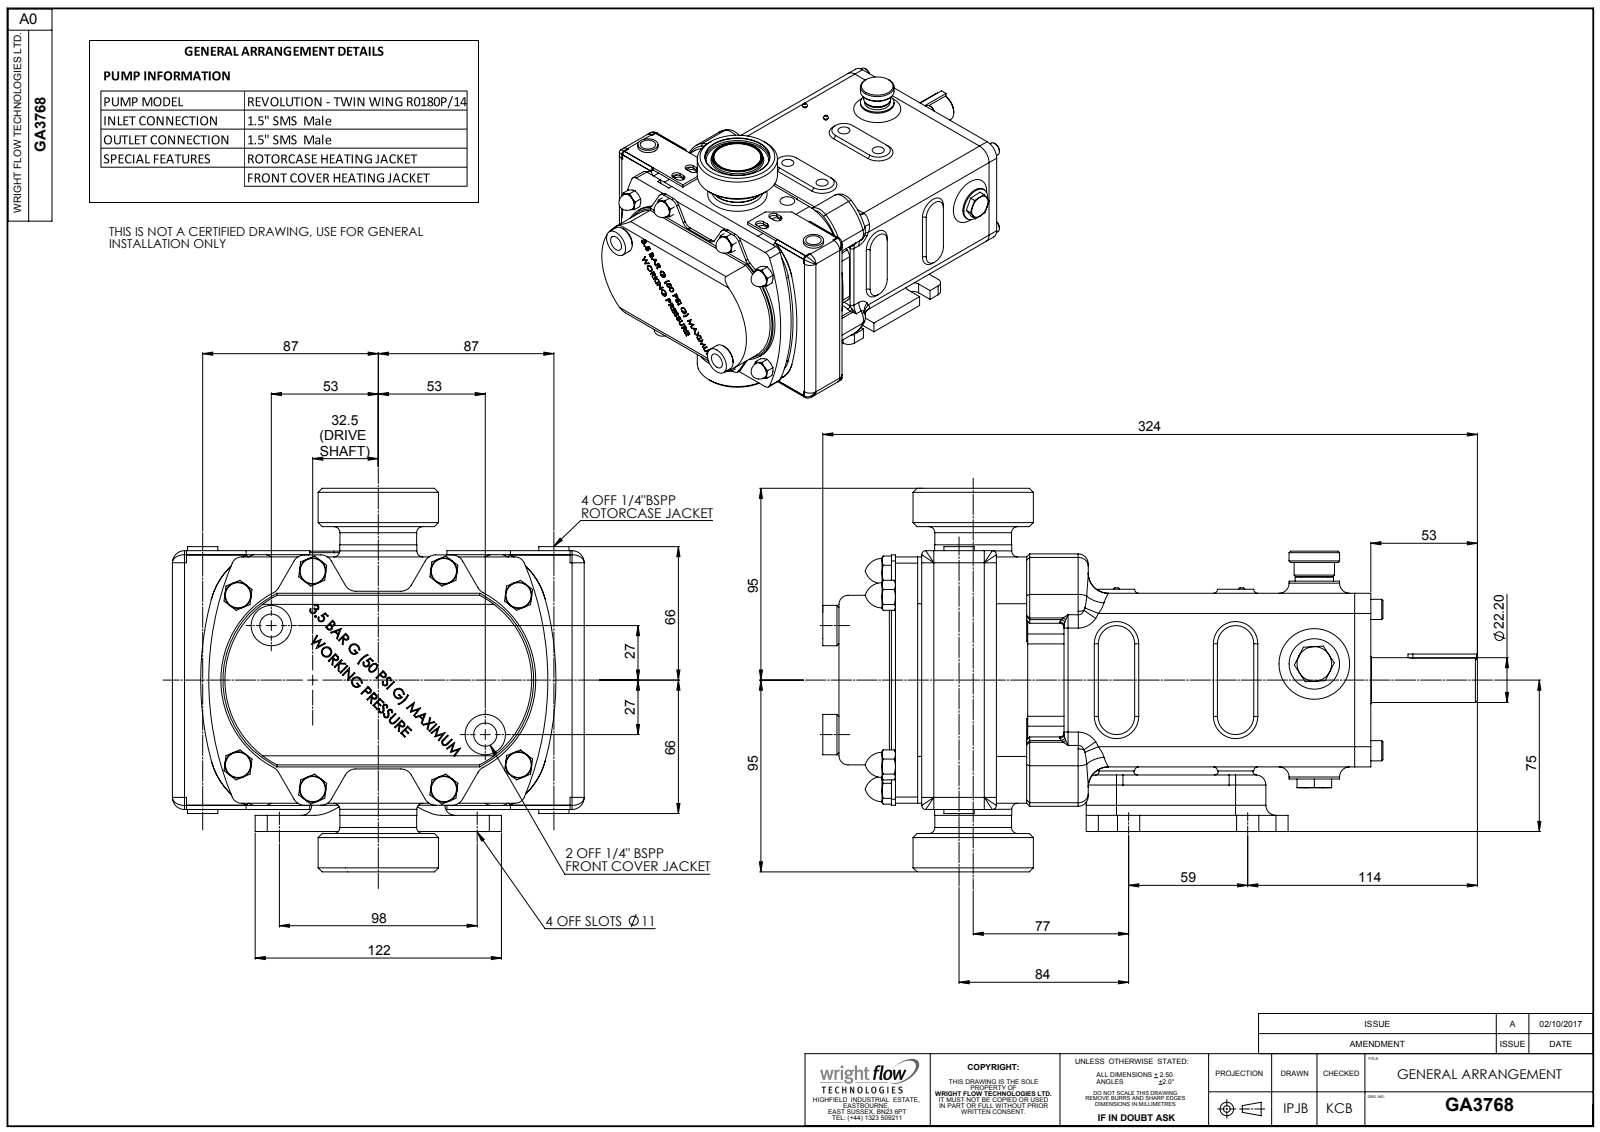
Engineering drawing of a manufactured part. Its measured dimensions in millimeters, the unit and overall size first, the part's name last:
Units: millimetres
Overall size (bounding box): 324.3 × 204 × 190
Round holes (diameter × count): ⌀7 ×4, ⌀9 ×4, ⌀10 ×4, ⌀11.5 ×4, ⌀11 ×2, ⌀22.53 ×1, ⌀35 ×1, ⌀48 ×1
Round bosses / shafts (diameter × count): ⌀10 ×6, ⌀25 ×4, ⌀20 ×4, ⌀13 ×4, ⌀15 ×2, ⌀59.6 ×1, ⌀38.2 ×1, ⌀38 ×1
Partial cylindrical surfaces — rounded edges, fillets, slot ends (radius × count): R6 ×38, R2 ×32, R10 ×26, R5 ×19, R3.5 ×8, R4 ×8, R8 ×8, R31 ×8
Main face-to-face distances: 2, 86, 28, 6, 235.5, 18, 104, 177.5, 14, 263.5
Hole centre spacings: 65, 14, 26.61, 33.9, 36, 38.16, 39.7, 43.1
Volume: 4 174 000 mm³ · Surface area: 363 718 mm²
Bodies: 6 solids, 2079 faces (859 planar, 471 cylindrical, 749 other)
Part name (STEP PRODUCT): Copy of Frame 2 R-C Bolt On Jacket^GA3768; Copy of Frame 2 Bolt on Jacket^GA3768; Copy of R0180 CPP V LHD^GA3768; GA3768 (+1 more)
STEP written by: SolidWorks 2023 (AUTOMOTIVE_DESIGN)
